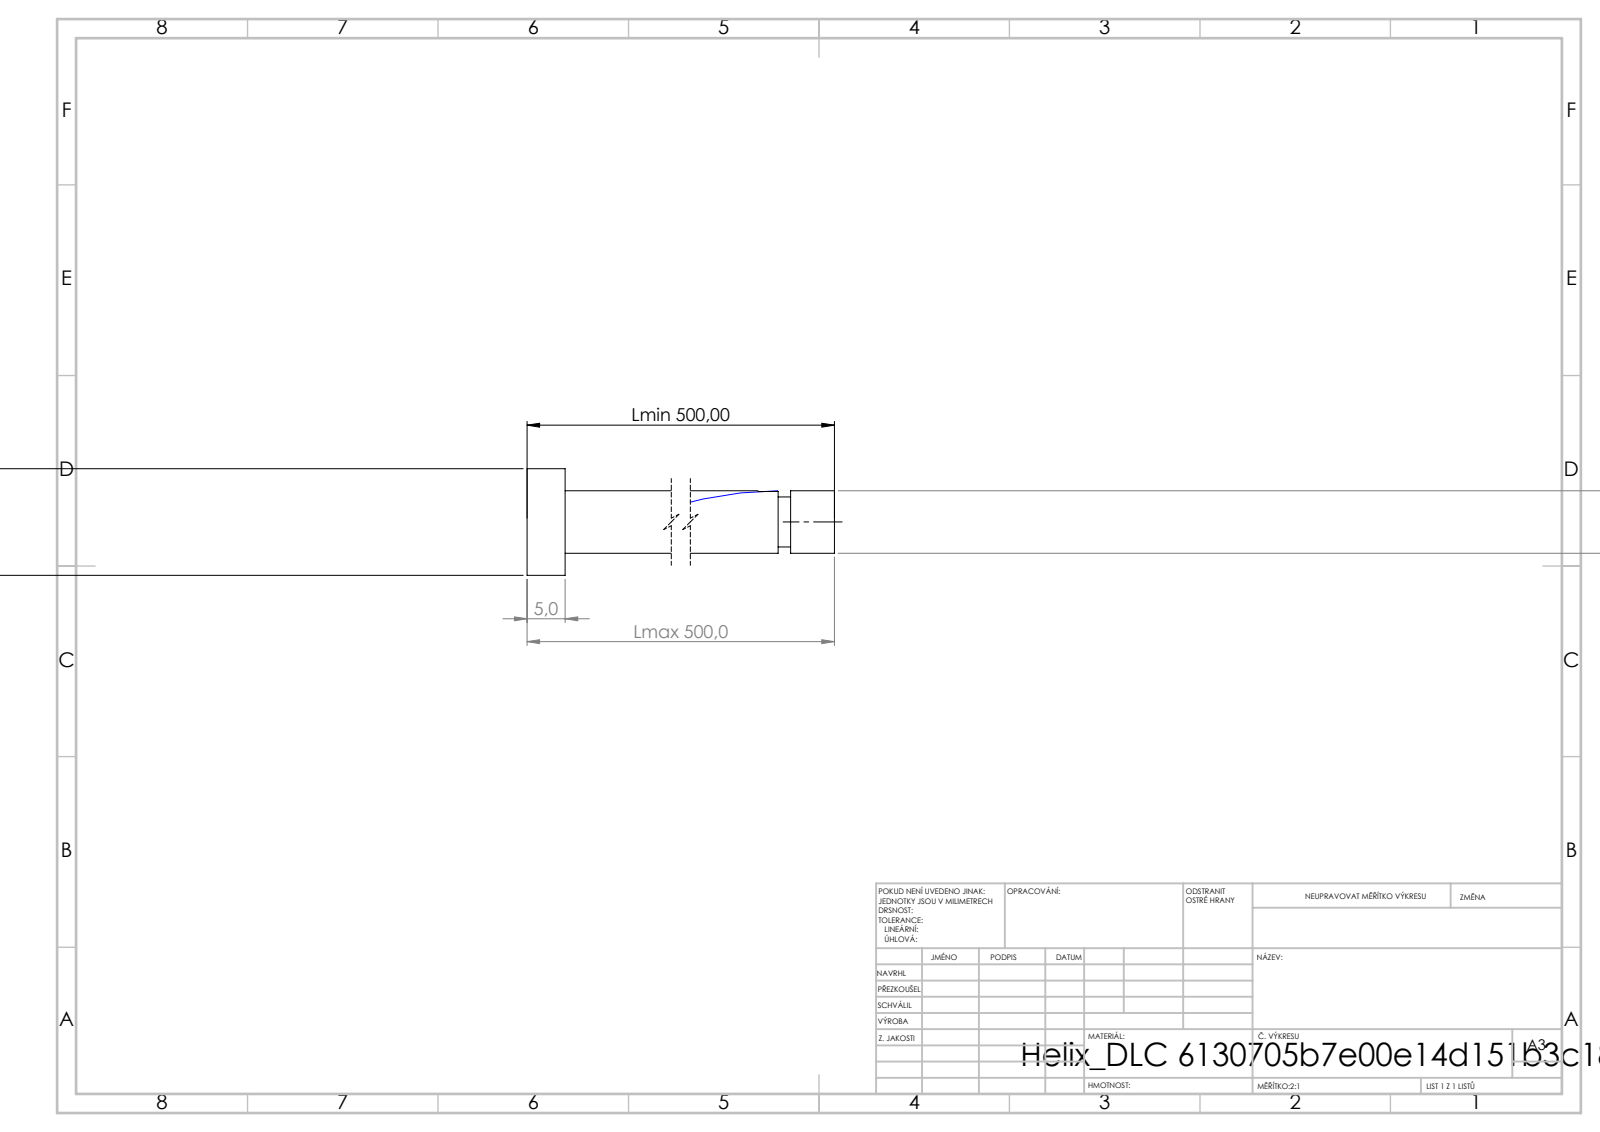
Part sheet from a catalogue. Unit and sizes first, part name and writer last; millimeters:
Units: millimetres
Overall size (bounding box): 500 × 14 × 14
Round bosses / shafts (diameter × count): ⌀14 ×1, ⌀8.2 ×1, ⌀6.56 ×1
Main face-to-face distances: 5, 500, 495, 494.25, 489.25, 5.75, 492.61, 487.61, 1.64, 7.39
Volume: 32 494 mm³ · Surface area: 17 808 mm²
Bodies: 1 solid, 16 faces (6 planar, 9 cylindrical, 1 other)
STEP written by: SolidWorks 2019 (CONFIG_CONTROL_DESIGN)
